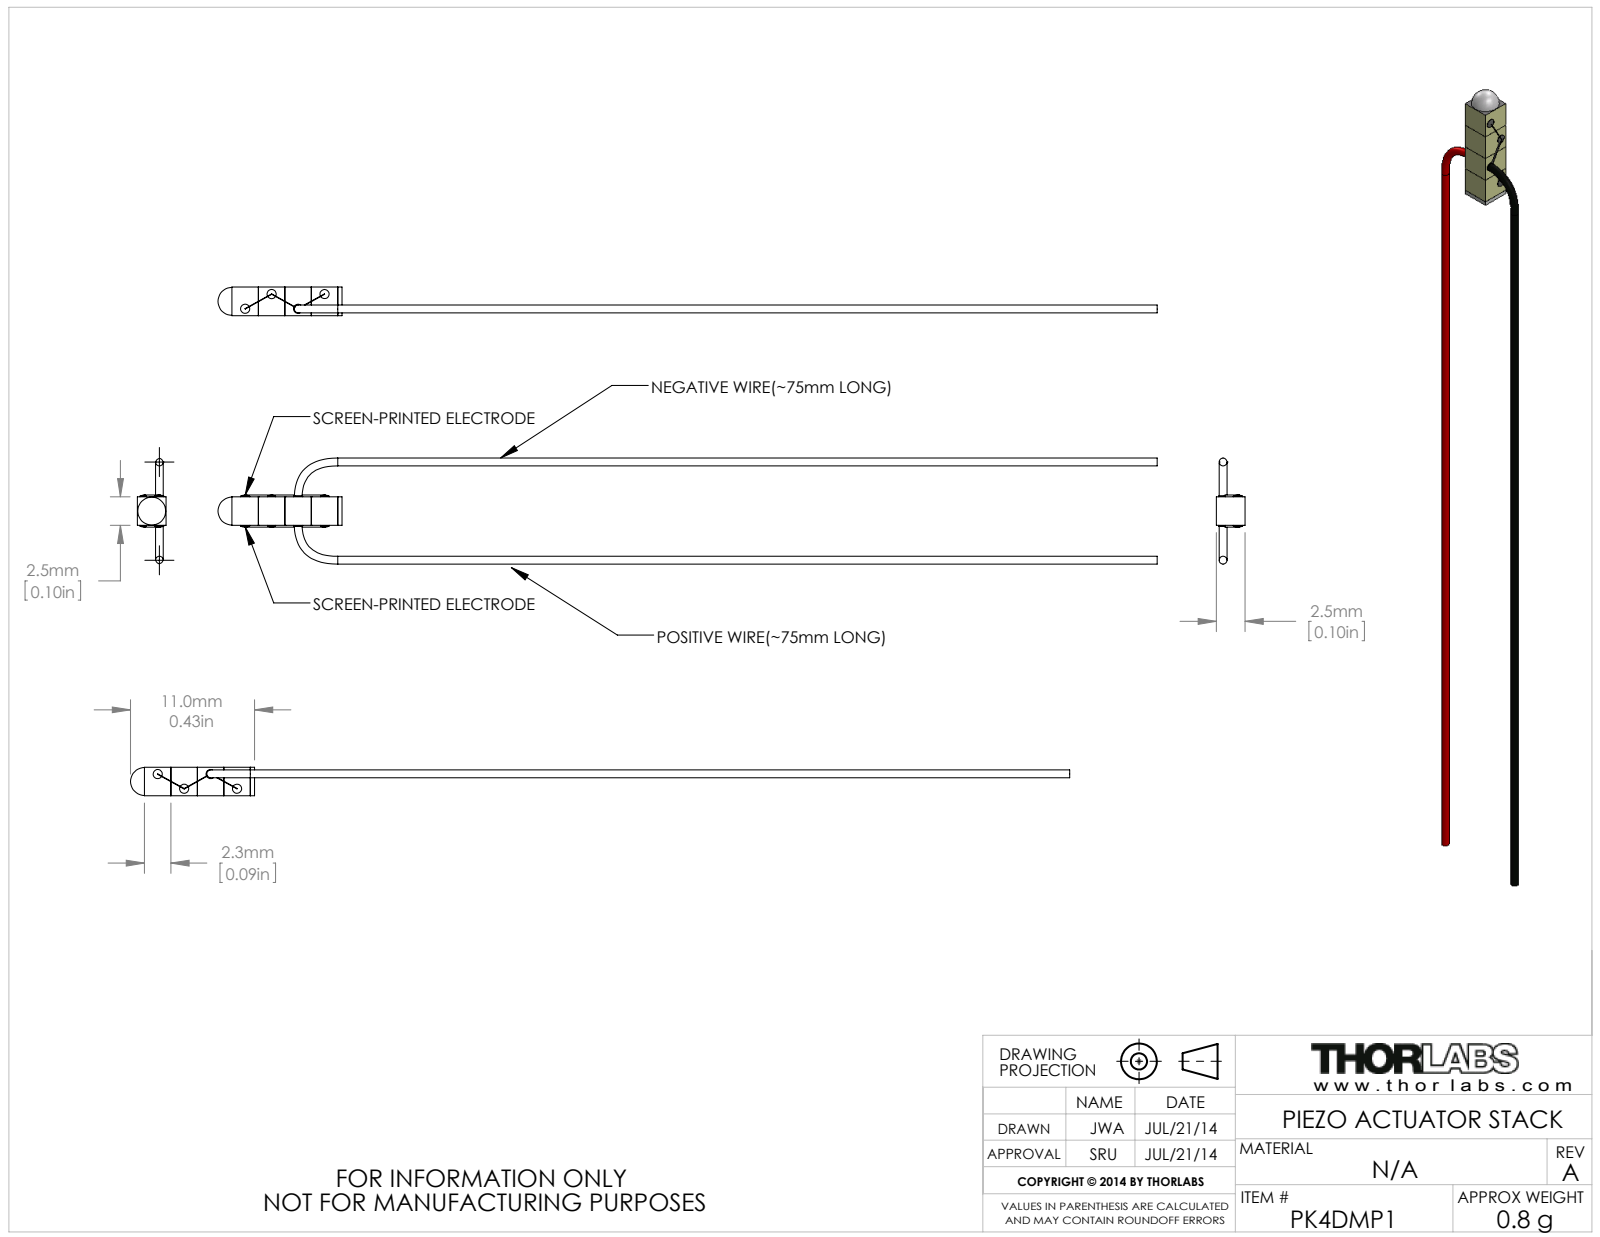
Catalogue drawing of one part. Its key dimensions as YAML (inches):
part_name: "PK4DMP1"
step_written_by: "SolidWorks 2012 (AUTOMOTIVE_DESIGN)"
units: inches
bodies: {solids: 2, faces: 128, planar: 66, cylindrical: 28, other: 34}
overall_size: [3.228, 0.364, 0.098]
volume: 0.007
surface_area: 0.767
round_bosses_or_shafts:
  - {diameter: 0.031, count: 4}
  - {diameter: 0.027, count: 2}
face_to_face_distances: [0.098, 0.091, 0.182, 0.091, 0.091, 0.273, 0.181, 0.182, 0.272, 0.015]
